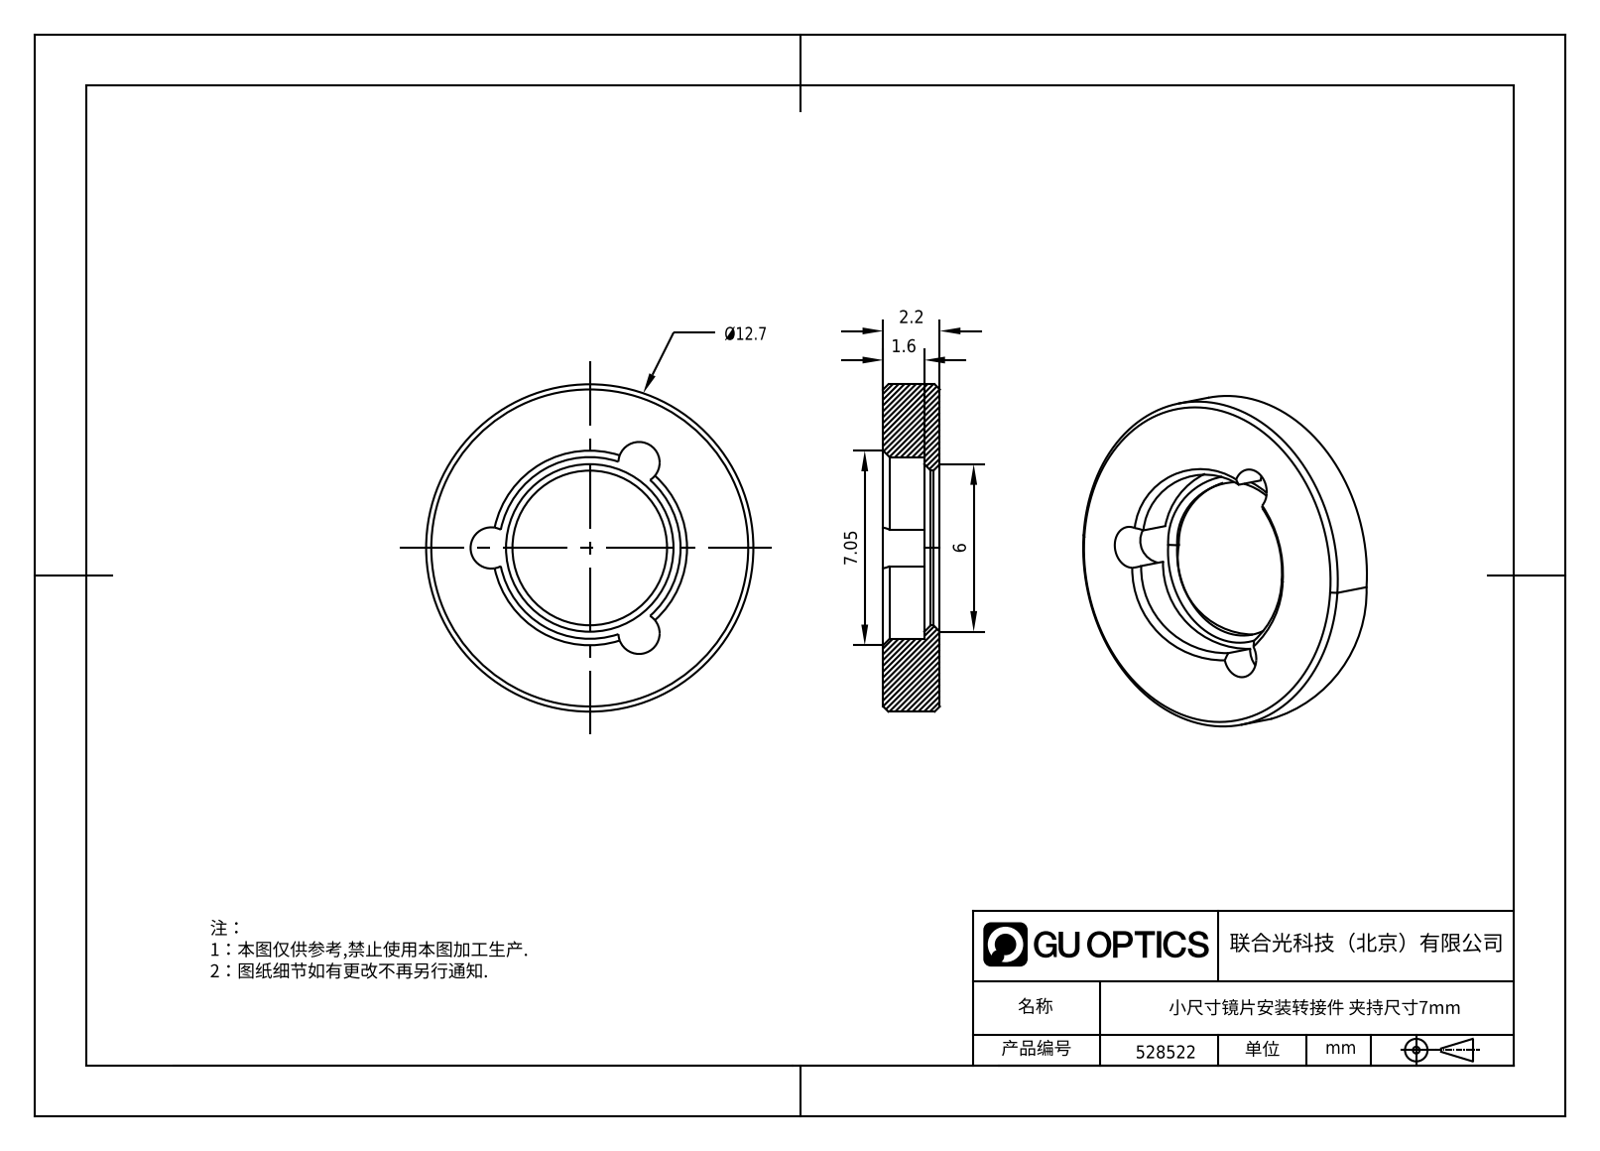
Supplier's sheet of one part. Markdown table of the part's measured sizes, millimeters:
| quantity | value |
| --- | --- |
| part name | 1.6.4.8-ZSJ-05-7 |
| STEP written by | SolidWorks 2021 (CONFIG_CONTROL_DESIGN) |
| units | millimeters |
| bodies | 1 solid, 28 faces (3 planar, 13 cylindrical, 12 other) |
| overall size | 12.7 × 12.7 × 2.2 |
| volume | 189 mm³ |
| surface area | 323 mm² |
| round holes (diameter × count) | 6 × 1, 7.05 × 1 |
| round bosses / shafts (diameter × count) | 12.7 × 1 |
| partial cylindrical surfaces (radius × count) | 0.8 × 3 |
| main face-to-face distances | 2.2, 0.6, 1.6 |
